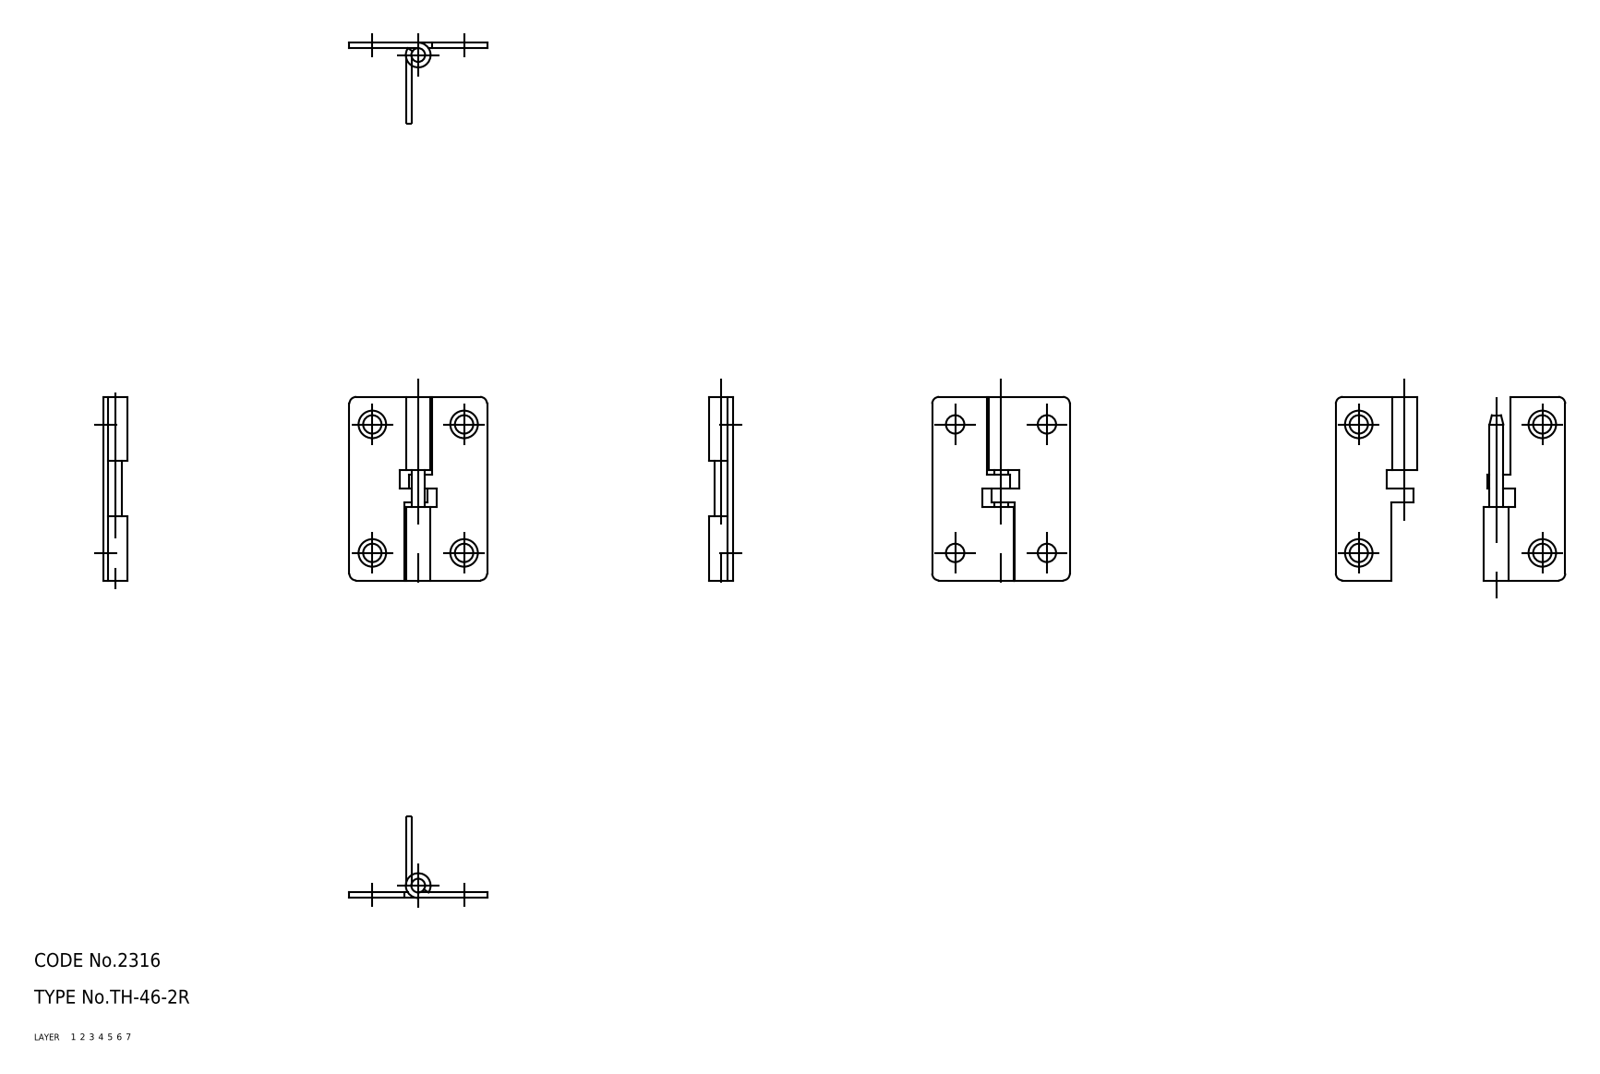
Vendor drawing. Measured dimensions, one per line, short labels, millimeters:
name: shaft; hinge piece_B; hinge piece_A; TH_46_2R_9597_36
written by: CADfix (AUTOMOTIVE_DESIGN)
unit: mm
bodies: 3 solids, 54 faces (0 planar, 0 cylindrical, 54 other)
size: 40 × 30 × 5.4
volume: 1 878 mm³; area: 3 487 mm²
